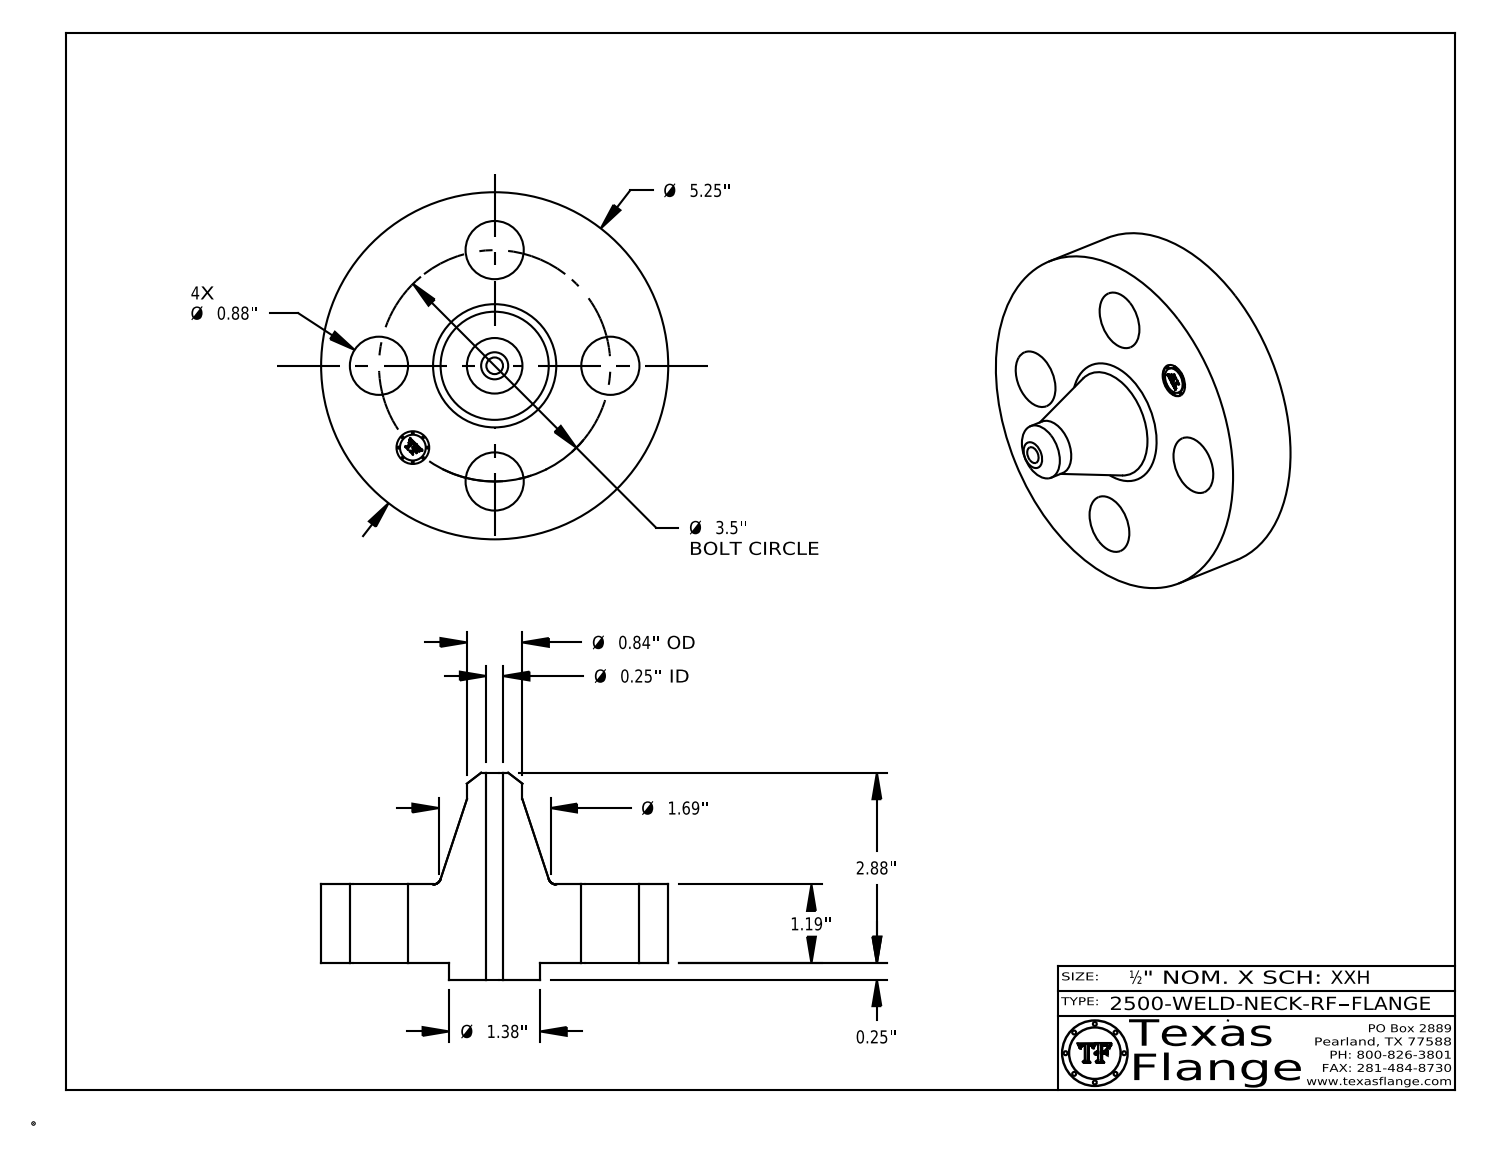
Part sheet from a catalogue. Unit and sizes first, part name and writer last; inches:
Units: inches
Overall size (bounding box): 5.25 × 5.25 × 3.13
Round holes (diameter × count): ⌀0.88 ×4, ⌀0.252 ×1, ⌀0.495 ×1
Round bosses / shafts (diameter × count): ⌀0.03 ×8, ⌀5.25 ×1, ⌀1.38 ×1, ⌀0.84 ×1, ⌀0.39 ×1
Main face-to-face distances: 1.19, 0.25, 1.44, 3.13, 2.88, 1.69, 1.425, 1.175, 0.015, 1.705
Hole centre spacings: 1.75, 2.475, 1.339, 3.233, 3.5
Volume: 24.95 in³ · Surface area: 79.09 in²
Bodies: 1 solid, 411 faces (369 planar, 36 cylindrical, 6 other)
Part name (STEP PRODUCT): 2500-WELD-NECK-RF
STEP written by: CATIA V5 STEP AP214 (AUTOMOTIVE_DESIGN)
